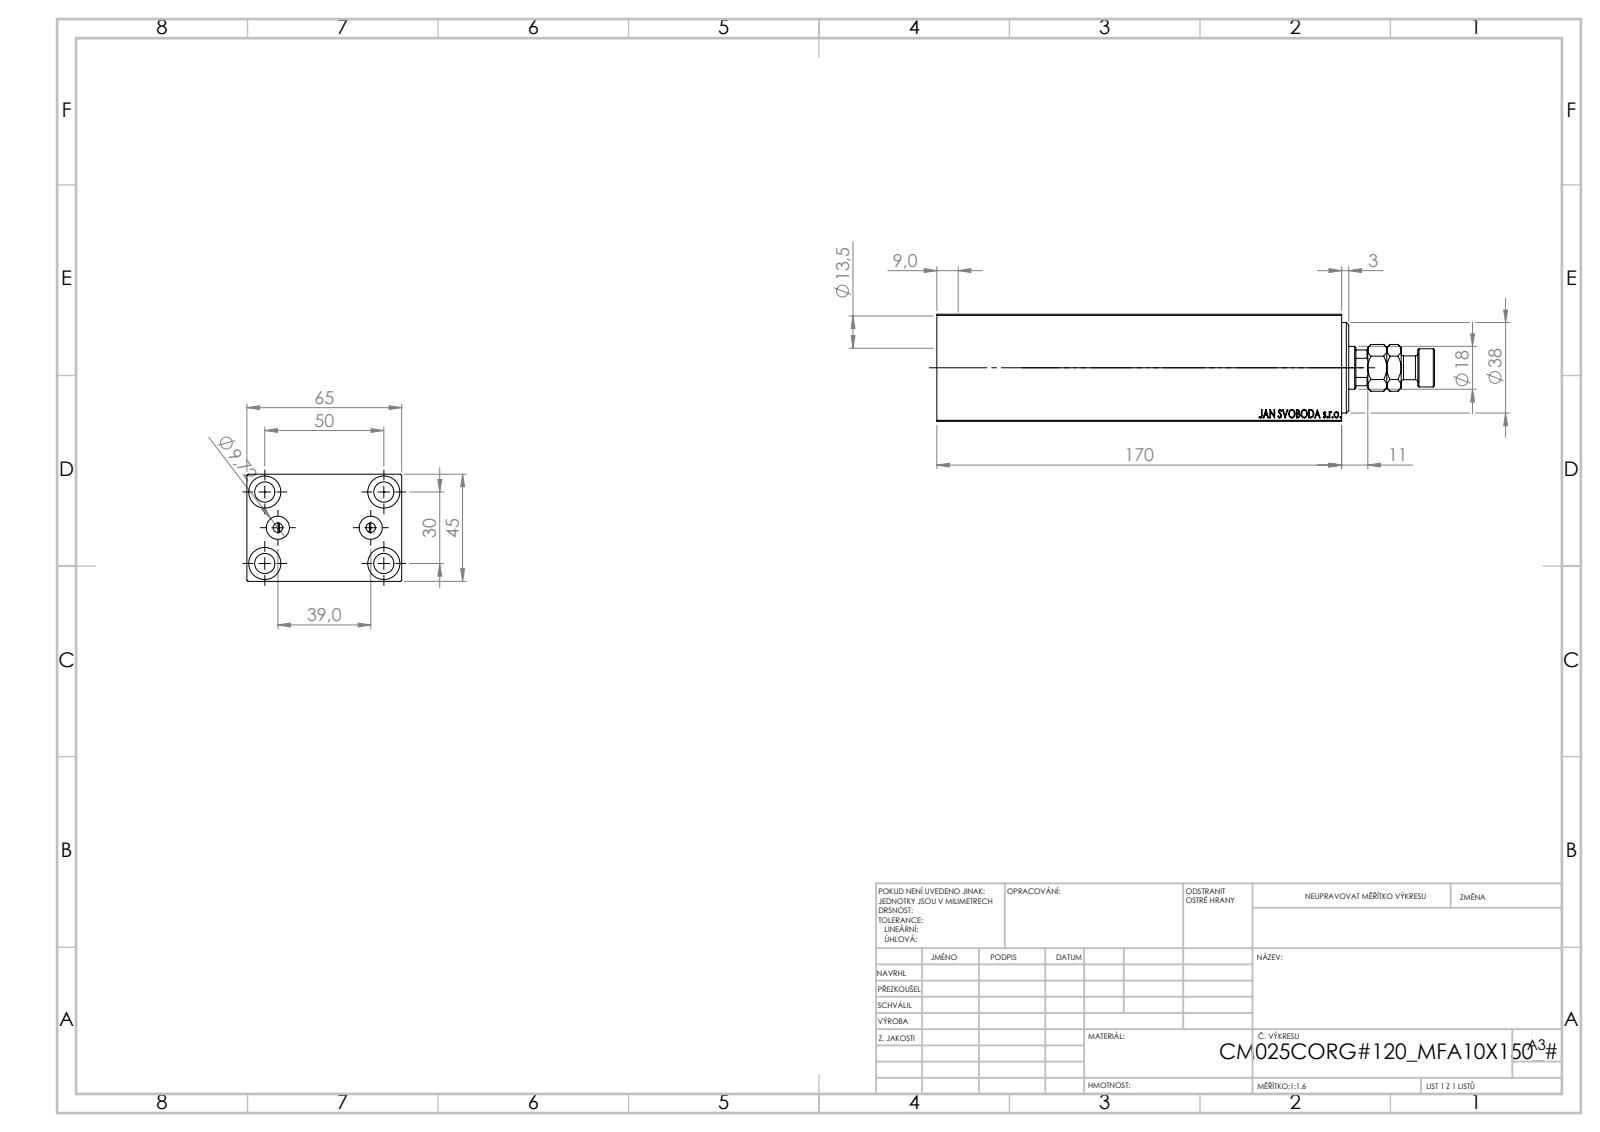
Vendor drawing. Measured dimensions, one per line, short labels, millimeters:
name: V450CM_VC_B; MFA; V450CM_C_VCP; V450CM_C_Body
written by: SolidWorks 2019 (CONFIG_CONTROL_DESIGN)
unit: mm
bodies: 4 solids, 910 faces (424 planar, 60 cylindrical, 426 other)
size: 209 × 65 × 45
volume: 428 016 mm³; area: 99 154 mm²
holes: 5× ⌀8.5, 4× ⌀13.5, 2× ⌀4, 2× ⌀9.72, 1× ⌀18, 1× ⌀21.5, 1× ⌀25, 1× ⌀27, 1× ⌀38
bosses: 1× ⌀16, 1× ⌀10
rounds: 1× R8.5
face distances: 45, 65, 164, 165, 5, 170, 3, 8, 6, 159
hole spacings: 15.98, 29.15, 46.96, 19.5, 30, 50, 58.31, 39
